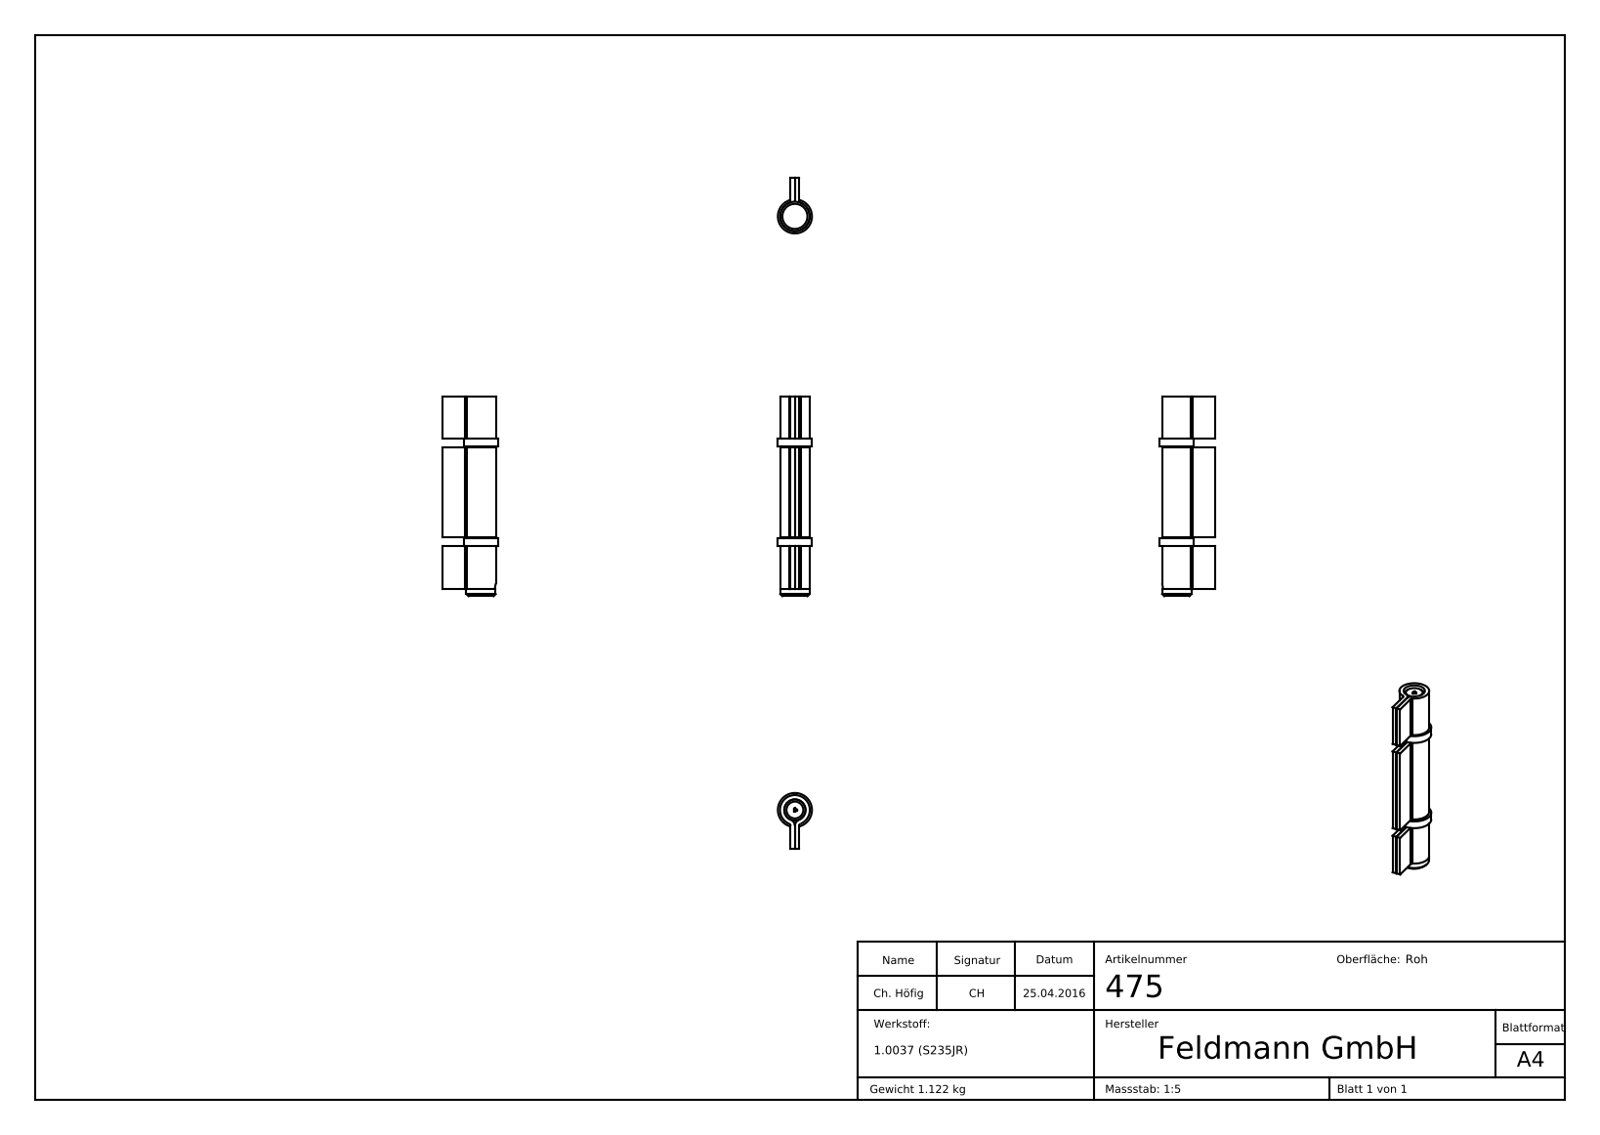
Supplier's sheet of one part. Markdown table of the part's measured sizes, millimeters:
| quantity | value |
| --- | --- |
| part name | 475 Teil2; 475 Teil1; 475; 475 Teil5 (+2 more) |
| STEP written by | SolidWorks 2018 (CONFIG_CONTROL_DESIGN) |
| units | millimeters |
| bodies | 6 solids, 213 faces (128 planar, 27 cylindrical, 58 other) |
| overall size | 187.7 × 52 × 32 |
| volume | 143 854 mm³ |
| surface area | 60 161 mm² |
| round holes (diameter × count) | 20 × 1, 20.15 × 1 |
| round bosses / shafts (diameter × count) | 32 × 1, 28 × 1, 27.5 × 1, 27.2 × 1, 19.8 × 1 |
| partial cylindrical surfaces (radius × count) | 2 × 2, 6 × 2, 5 × 1 |
| main face-to-face distances | 4, 4.1, 8.1, 8.35, 92.35, 40, 48.35, 132.35, 140.7, 100.7 |
